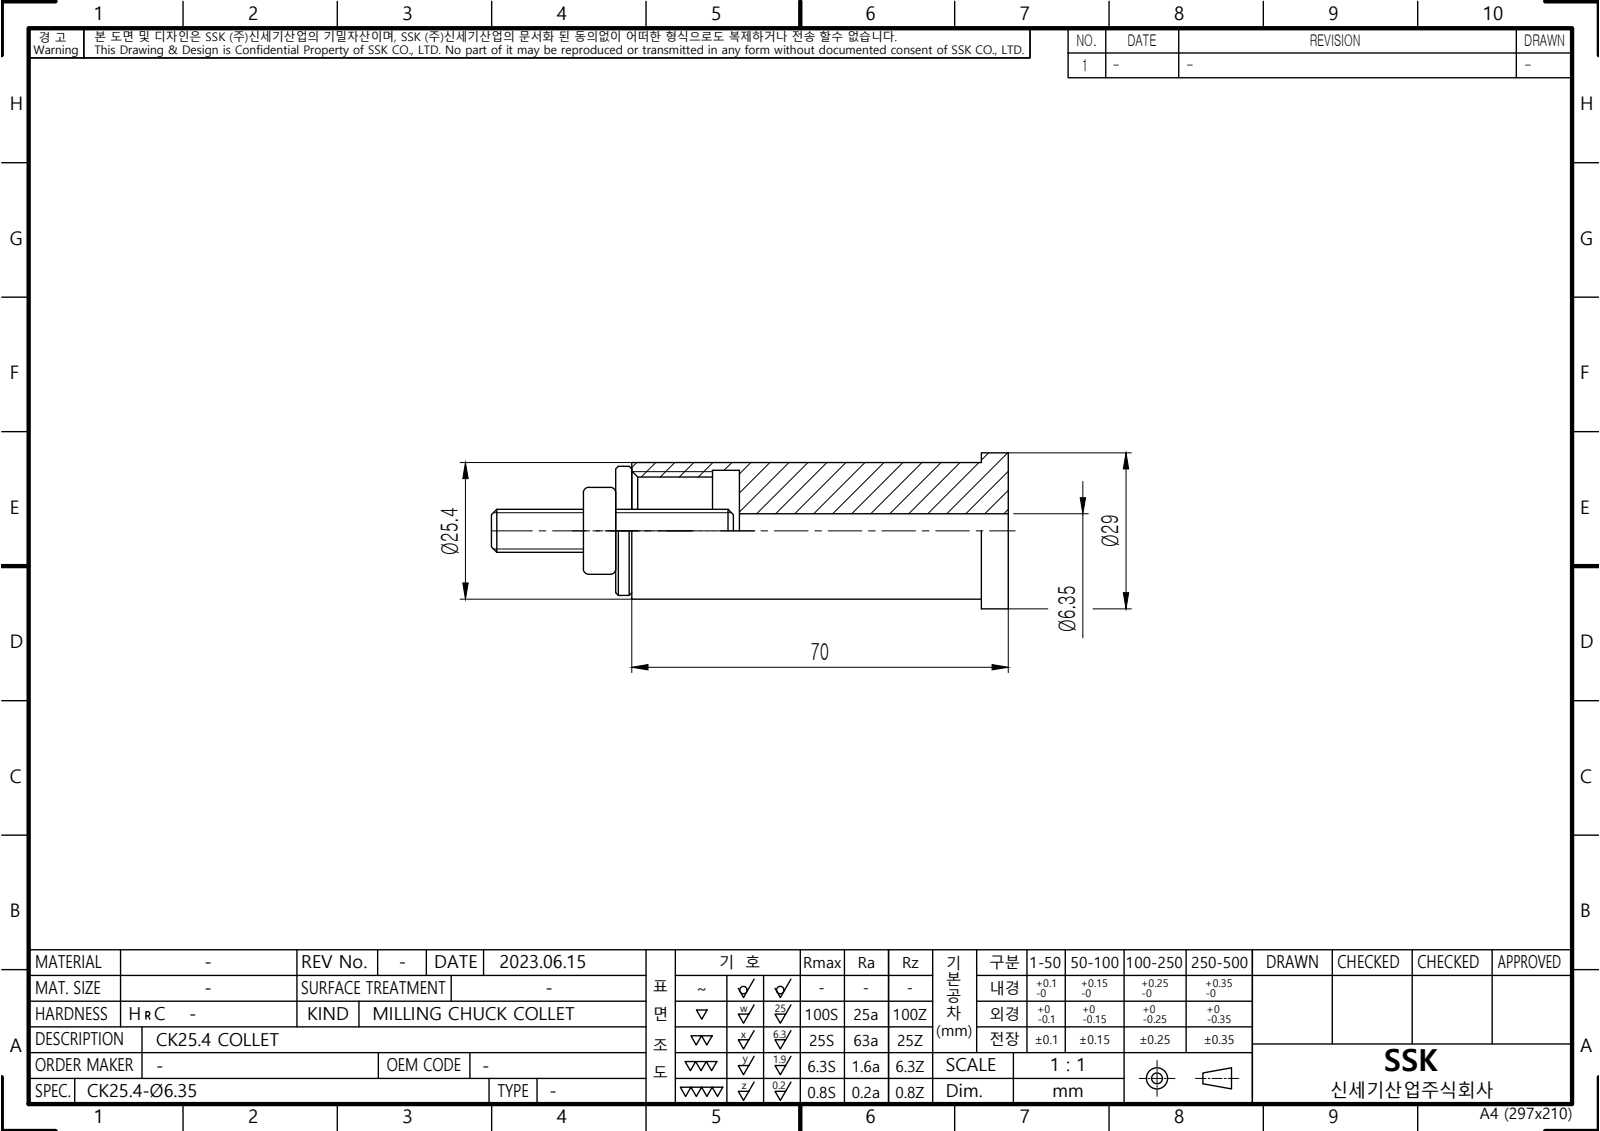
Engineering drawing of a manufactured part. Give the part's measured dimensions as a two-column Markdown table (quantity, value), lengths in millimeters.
| quantity | value |
| --- | --- |
| part name | LO-CK19.05-6 |
| STEP written by | Autodesk Inventor 2022 (AUTOMOTIVE_DESIGN) |
| units | millimeters |
| bodies | 1 solid, 10 faces (5 planar, 5 cylindrical, 0 other) |
| overall size | 70 × 29 × 29 |
| volume | 27 512 mm³ |
| surface area | 9 345 mm² |
| round holes (diameter × count) | 6.35 × 1, 20.92 × 1, 22.5 × 1 |
| round bosses / shafts (diameter × count) | 29 × 1, 25.4 × 1 |
| main face-to-face distances | 50, 5, 20, 70, 65, 45, 15, 55 |
